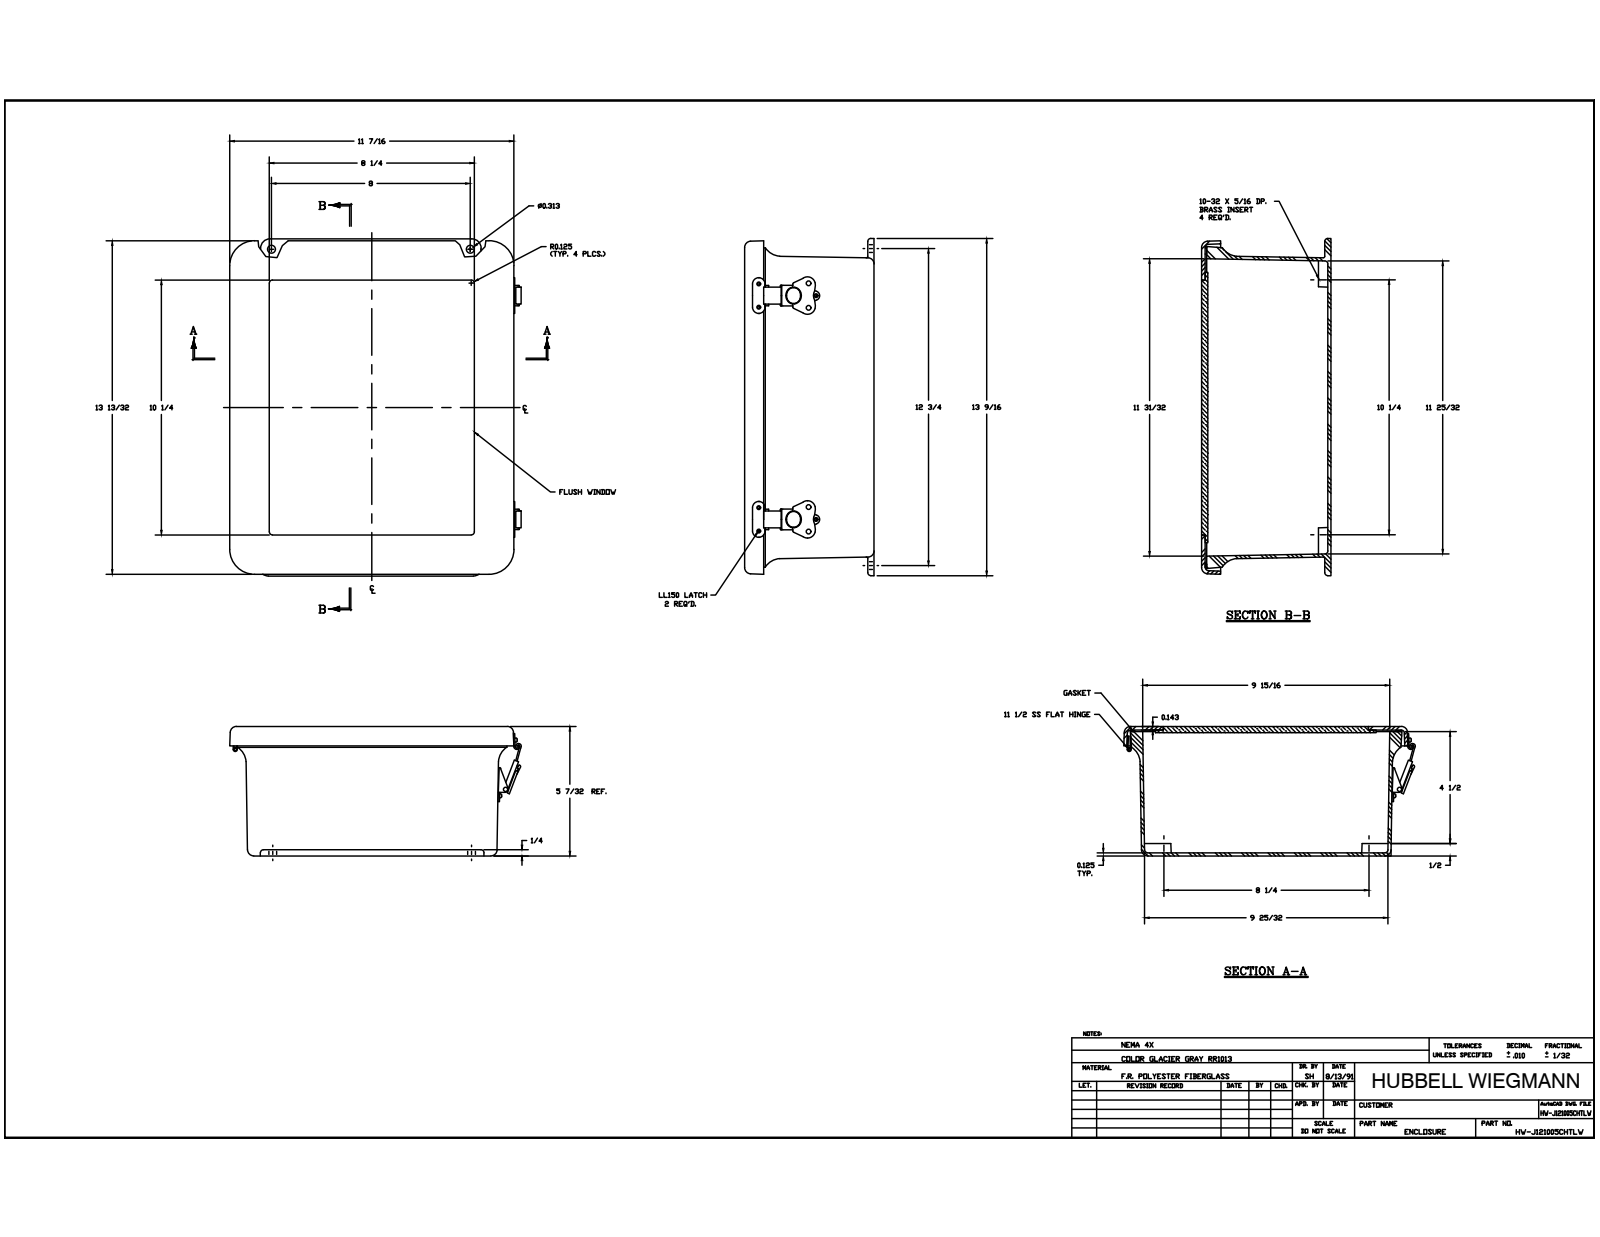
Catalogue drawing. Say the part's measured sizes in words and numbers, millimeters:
The part is named "J1210HL_5; RMINS45821P_143; RMINS45821P_144; RMINS45821P_145 (+8 more)". Its 3-D file was written by "Autodesk Inventor 2014 (AUTOMOTIVE_DESIGN)". It is 49 solids with 1172 faces: 528 planar, 453 cylindrical and 191 other. Overall it measures 344.49 by 295.51 by 132.56 millimeters. Its volume is 1 599 000 cubic millimeters and its surface area 796 061 square millimeters. Round holes: 16 of diameter 3.56, 8 of diameter 3.33, 5 of diameter 3.86, 4 of diameter 3.3, 4 of diameter 3.96, 4 of diameter 4.2, 4 of diameter 5, 4 of diameter 5.54, 2 of diameter 3, 2 of diameter 3.5, 2 of diameter 4.61, 2 of diameter 4.62. Round bosses or shafts: 16 of diameter 6.35, 16 of diameter 3.17, 4 of diameter 6.86, 2 of diameter 14.8, 2 of diameter 13.3, 2 of diameter 5.3, 2 of diameter 4.7, 2 of diameter 3.25. Partial cylindrical surfaces (rounded edges, fillets, slot ends): 20 of radius 0.79, 19 of radius 2, 16 of radius 3.17, 12 of radius 6.35, 8 of radius 1, 8 of radius 1.15, 8 of radius 1.2, 8 of radius 2.18. The main face-to-face distances are 3.17, 132.56, 6.35, 129.39, 126.21, 123.04, 128.93, 125.76, 2.72, 3.63. The hole center spacings are 228.6, 20.99, 92.08, 7, 15.65, 17.8, 23.82, 34.24.
